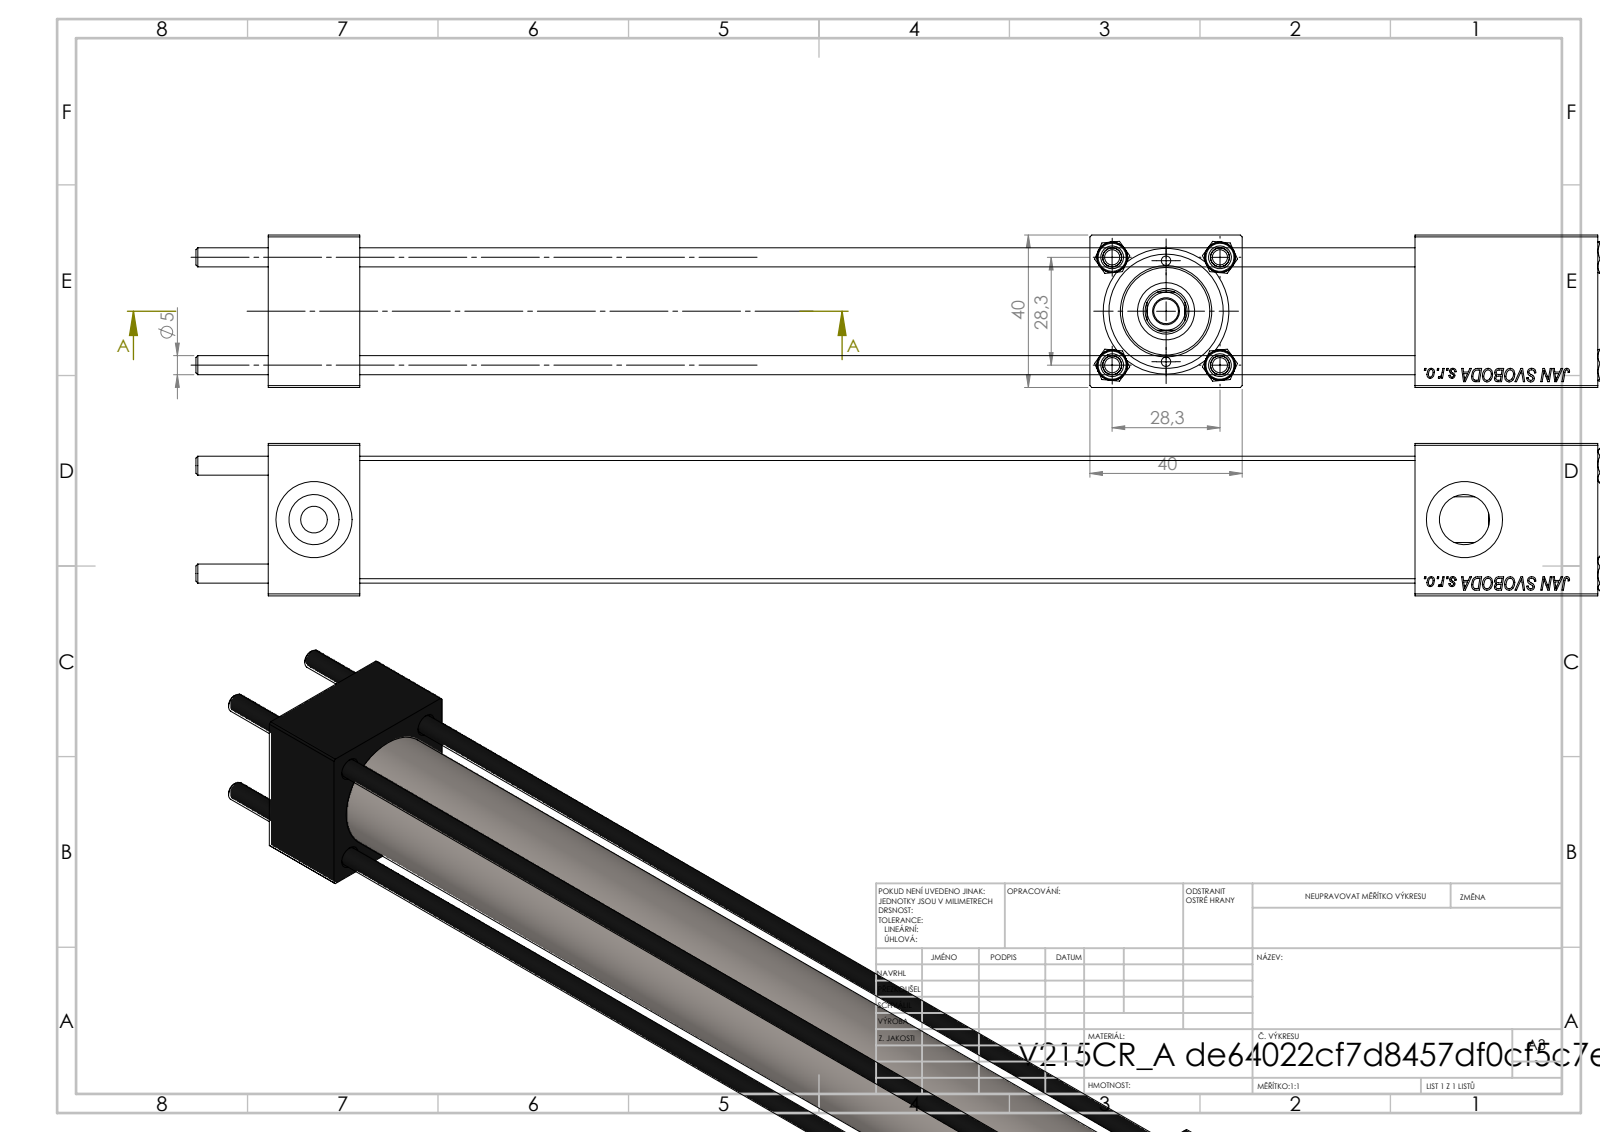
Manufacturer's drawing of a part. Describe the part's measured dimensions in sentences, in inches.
The part is named "CR025_012_A_0_G_A_G_M_020_+#_##_TYCINKA; NUT_M5; V215CR_VCP; V215CR_BODY_A (+1 more)". Its 3-D file was written by "SolidWorks 2019 (CONFIG_CONTROL_DESIGN)". It is 11 solids with 1137 faces: 519 planar, 82 cylindrical and 536 other. Overall it measures 15.079 by 1.575 by 1.575 inches. Its volume is 15.23 cubic inches and its surface area 189.9 square inches. Round holes: 4 of diameter 0.197, 3 of diameter 0.787, 2 of diameter 0.098, 2 of diameter 0.276, 2 of diameter 0.518, 1 of diameter 0.256, 1 of diameter 0.472, 1 of diameter 0.591, 1 of diameter 0.984, 1 of diameter 1.181. Round bosses or shafts: 4 of diameter 0.315, 1 of diameter 1.22, 1 of diameter 0.945. Partial cylindrical surfaces (rounded edges, fillets, slot ends): 1 of radius 0.217. The main face-to-face distances are 1.575, 0.945, 12.61, 11.665, 13.74, 12.795, 1.13, 11.85, 10.906, 0.76. The hole center spacings are 0.558, 0.788, 1.114, 1.214, 0.522, 1.576, 1.043, 11.89.
